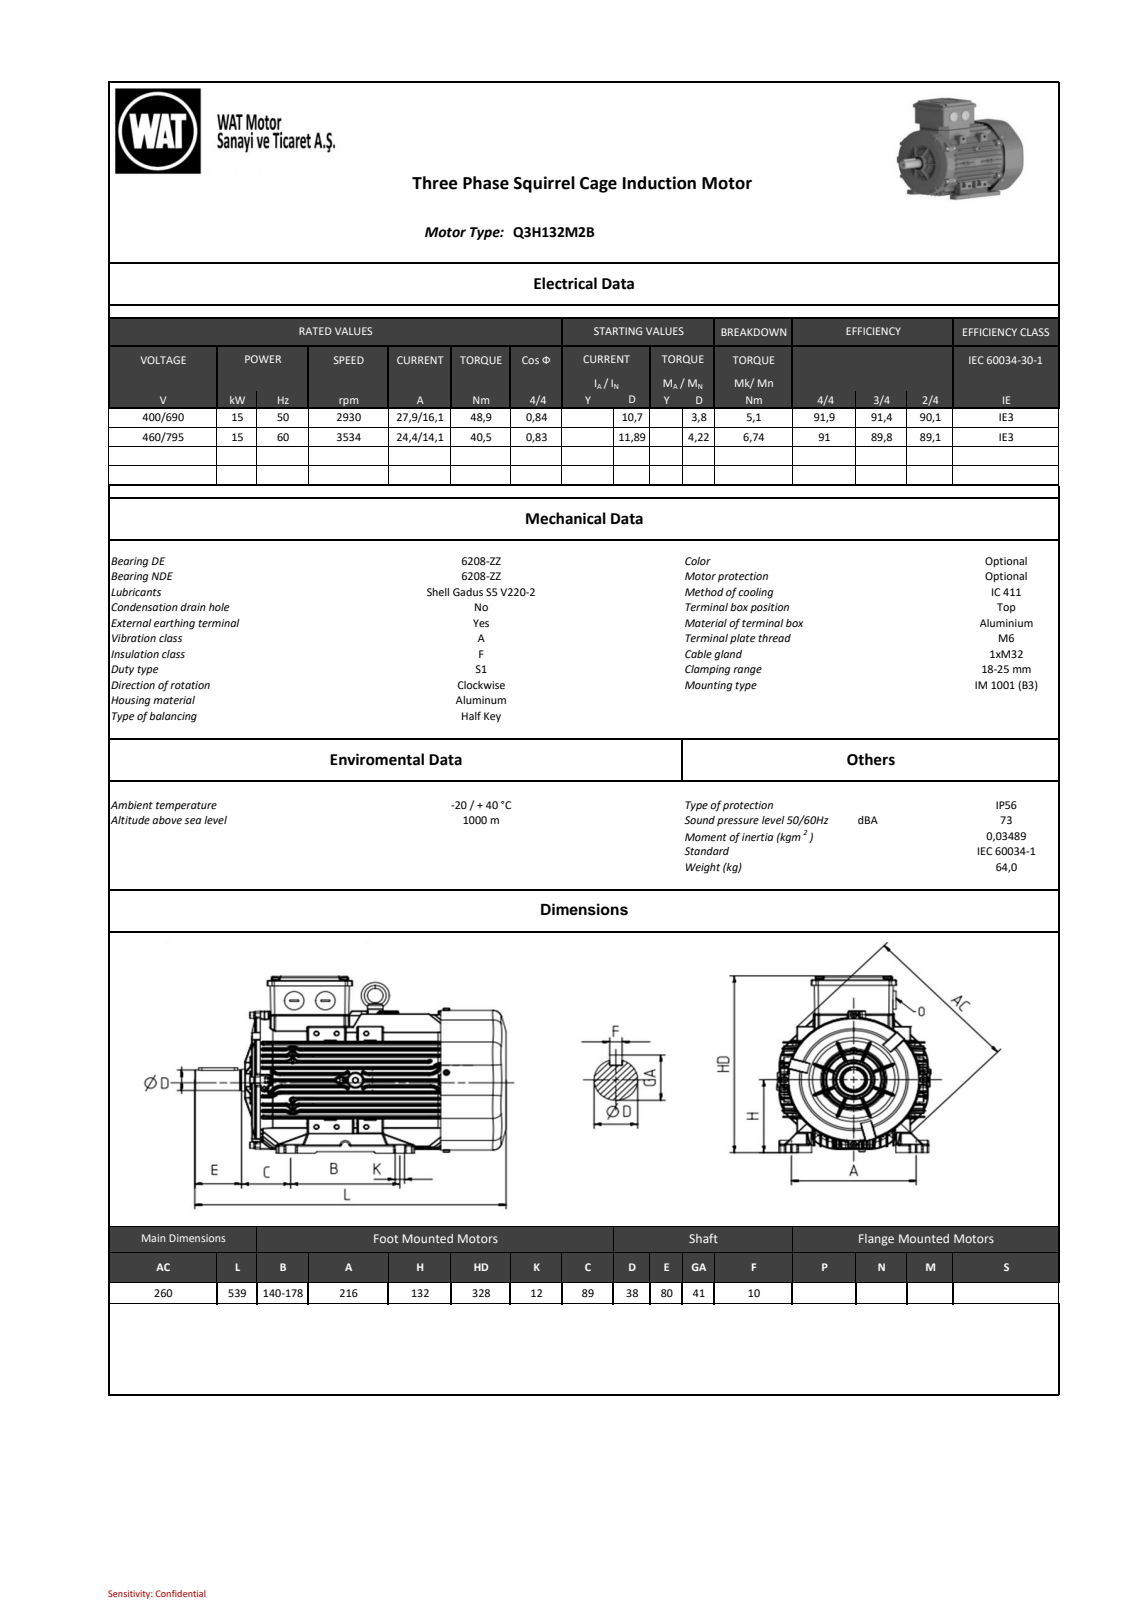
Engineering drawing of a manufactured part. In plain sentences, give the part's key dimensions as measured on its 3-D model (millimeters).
The part is named "26000438DCC3wi7p". Its 3-D file was written by "SIEMENS PLM Software NX 11.0 (AUTOMOTIVE_DESIGN)". It is 0 solids with 16059 faces: 3333 planar, 4989 cylindrical and 7737 other. Overall it measures 538.83 by 322.2 by 266.14 millimeters. Round holes: 8 of diameter 5.5, 8 of diameter 6.65, 8 of diameter 8.5, 6 of diameter 4, 3 of diameter 4.2, 2 of diameter 8.03, 2 of diameter 8.47, 2 of diameter 8.48, 2 of diameter 15, 2 of diameter 28, 2 of diameter 30.4, 1 of diameter 5.6. Round bosses or shafts: 14 of diameter 8, 8 of diameter 13, 6 of diameter 4.2, 4 of diameter 13.4, 3 of diameter 38, 2 of diameter 32, 2 of diameter 8.5, 1 of diameter 230.5. Partial cylindrical surfaces (rounded edges, fillets, slot ends): 1497 of radius 0.8, 1352 of radius 1, 122 of radius 0.1, 110 of radius 2, 79 of radius 0.5, 41 of radius 1.5, 38 of radius 3, 18 of radius 0.2. The main face-to-face distances are 10.42, 1.5, 10.56, 3, 10.28, 20.84, 125.58, 115.18, 104.9, 94.46. The hole center spacings are 97.42, 62.23, 88, 12.73, 74.95, 106, 120.5, 137.18.
